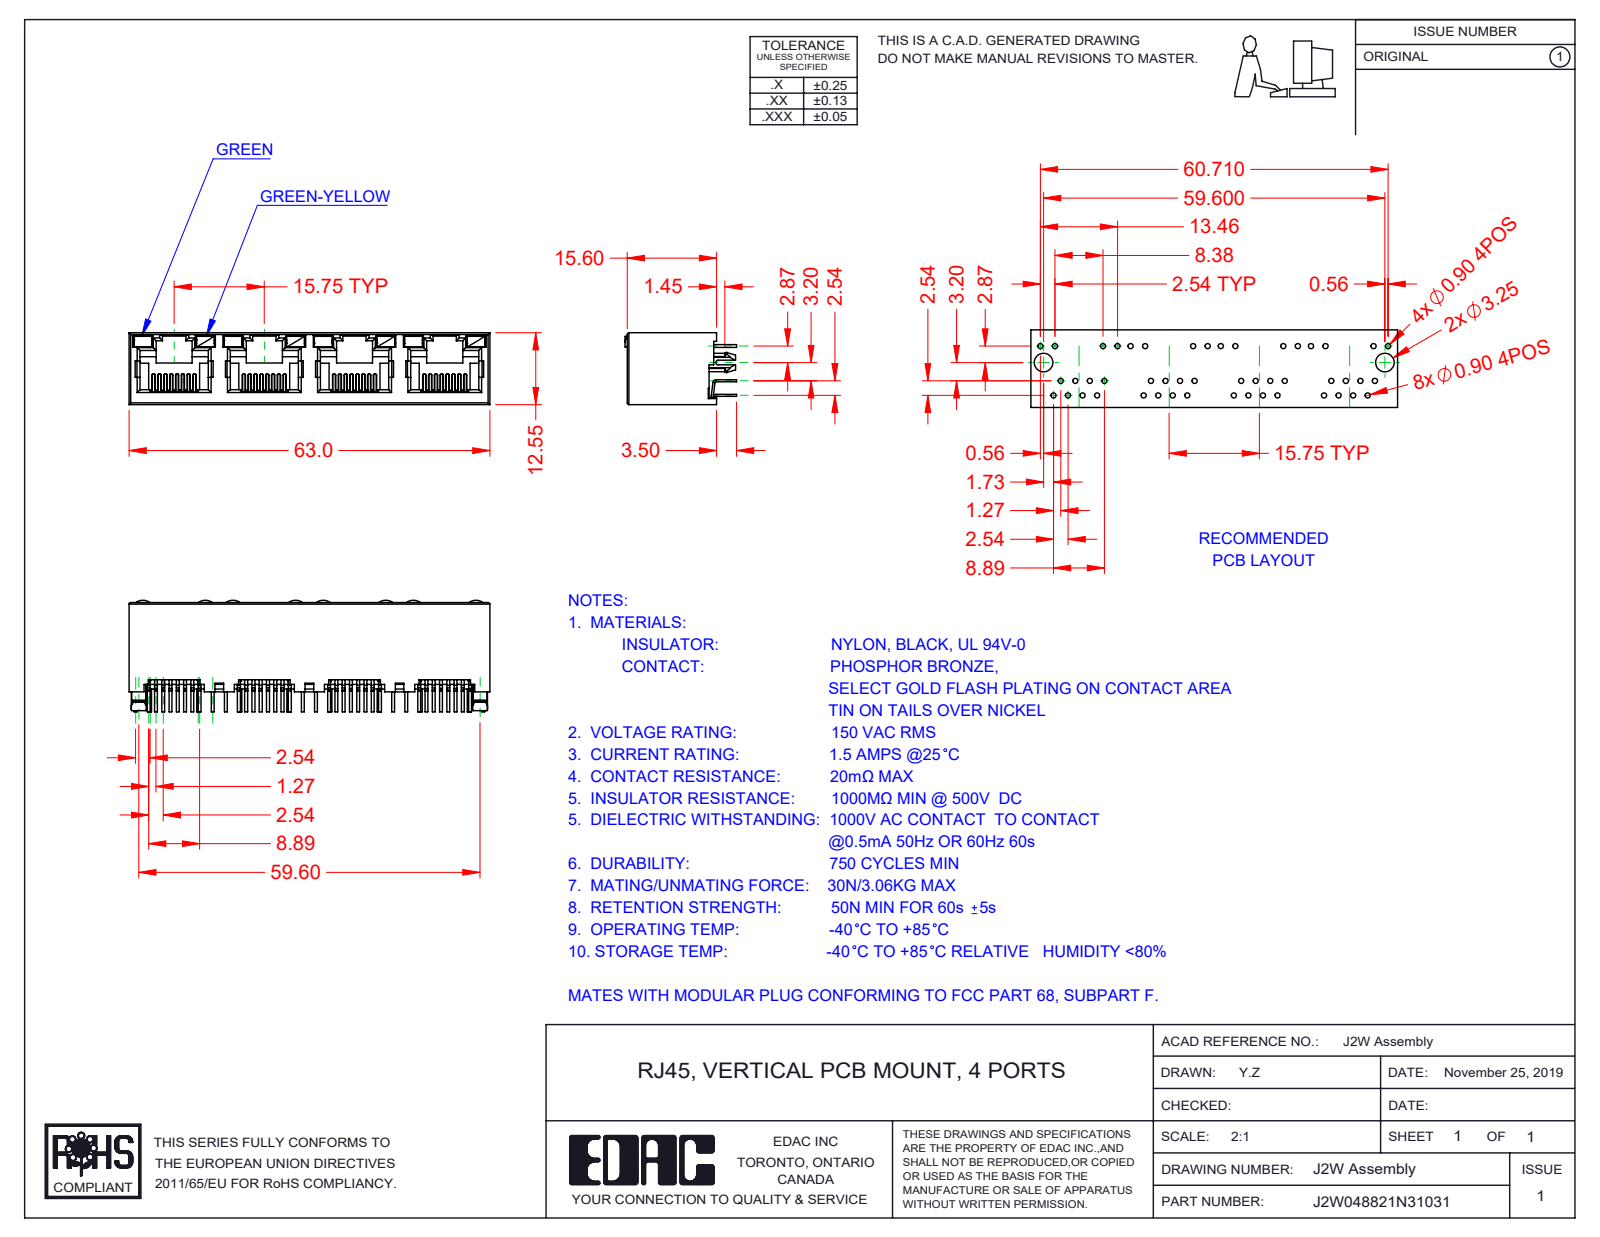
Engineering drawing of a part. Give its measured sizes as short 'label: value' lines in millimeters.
name: 2W LED RH_5-Green-Yellow; 2W Contacts; 2W Insulator; 2W LED LH_3-Green (+2 more)
written by: SolidWorks 2016 (CONFIG_CONTROL_DESIGN)
unit: mm
bodies: 45 solids, 3139 faces (2600 planar, 481 cylindrical, 58 other)
size: 63 × 19.5 × 12.55
volume: 5 335 mm³; area: 13 144 mm²
rounds: 64× R0.15, 29× R0.2, 28× R0.5, 14× R0.3, 8× R0.45, 8× R2, 2× R0.25, 2× R1.5
face distances: 12.55, 11.9, 0.65, 15.75, 0.36, 1.5, 0.78, 0.6, 11.3, 31.5
